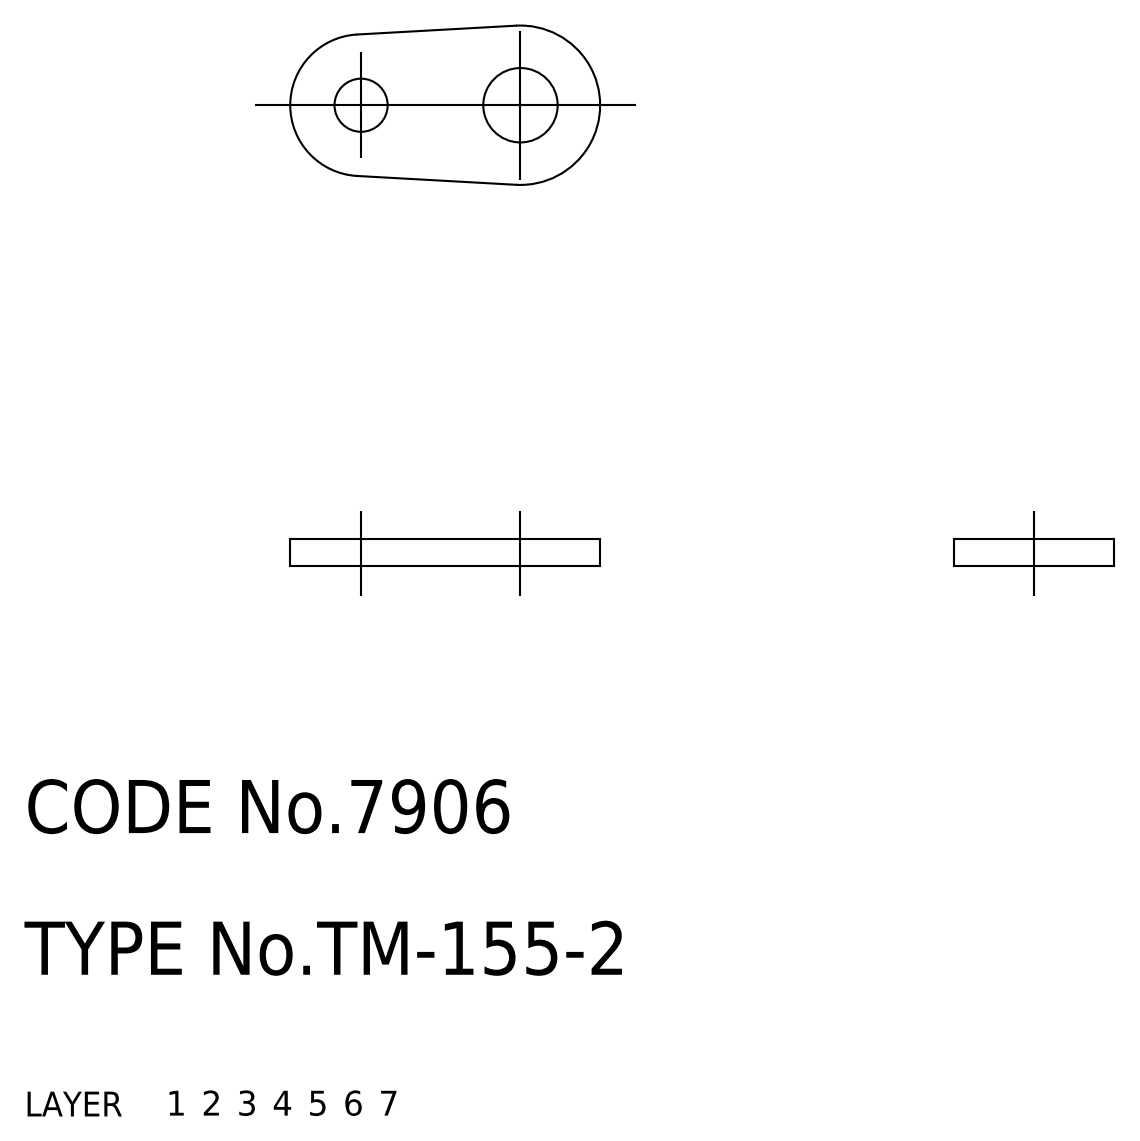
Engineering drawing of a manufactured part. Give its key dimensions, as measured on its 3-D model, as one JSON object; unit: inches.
{"part_name": "terminal", "step_written_by": "CADfix (AUTOMOTIVE_DESIGN)", "units": "inches", "bodies": {"solids": 1, "faces": 10, "planar": 0, "cylindrical": 0, "other": 10}, "overall_size": [0.689, 0.354, 0.059], "volume_in3": 0.01, "surface_area_in2": 0.505}
